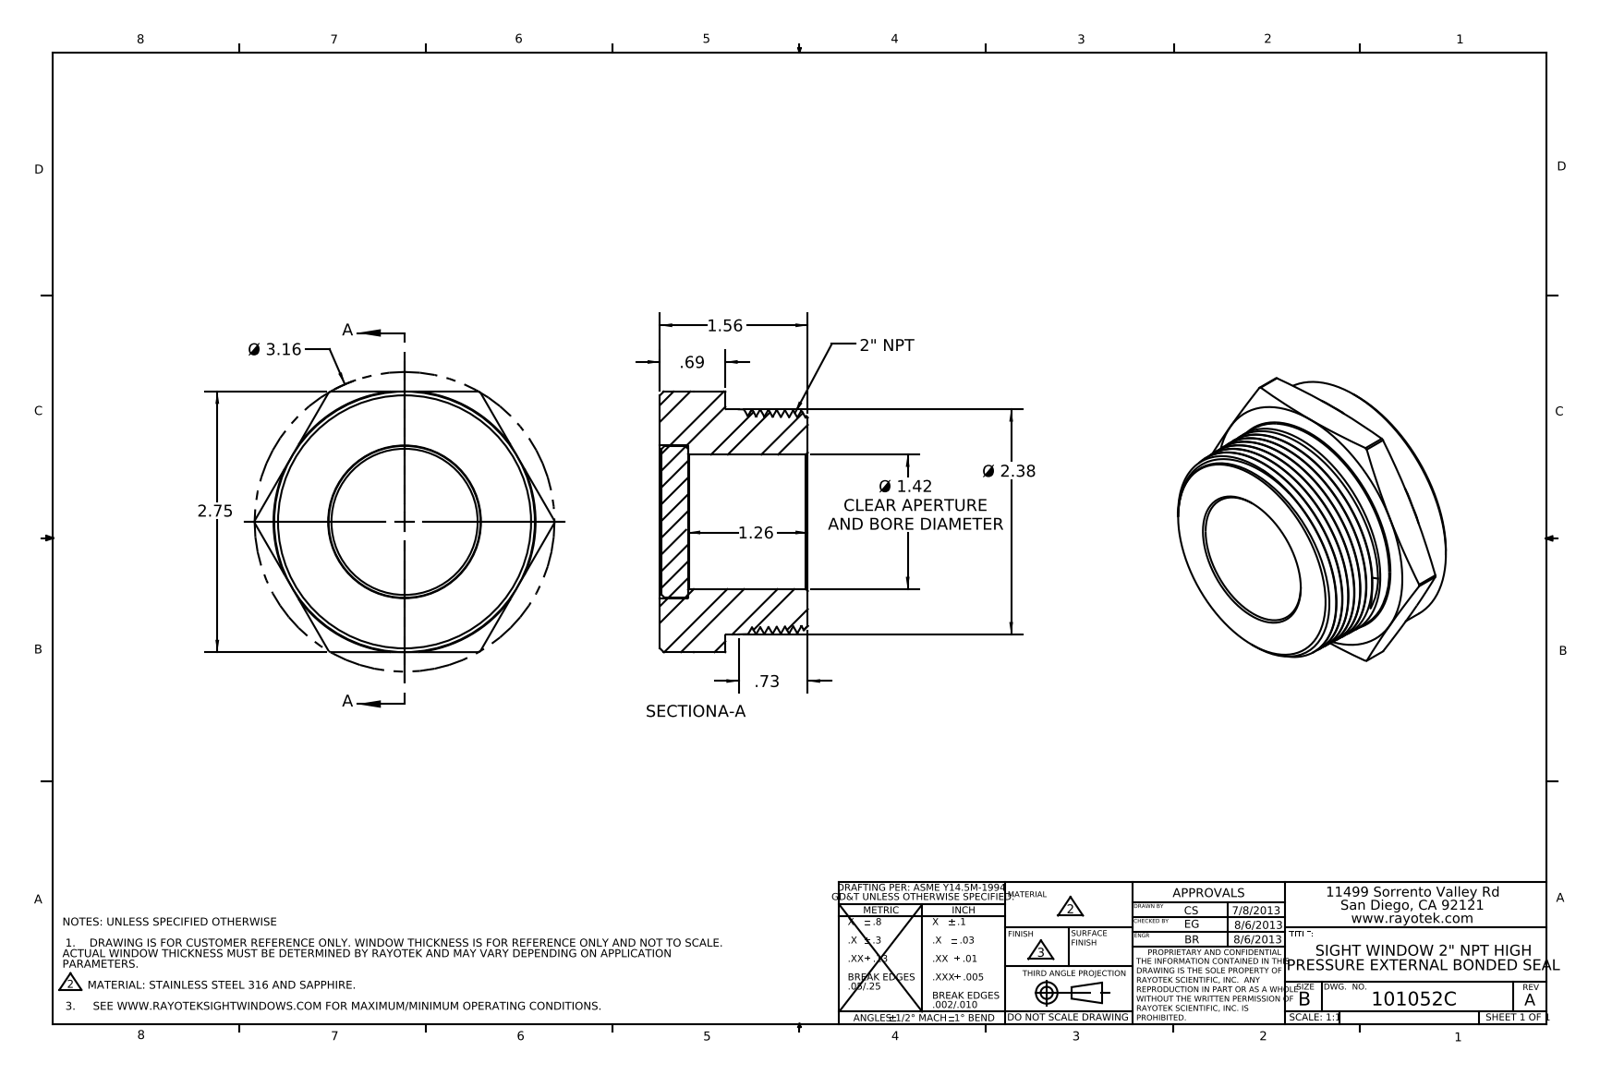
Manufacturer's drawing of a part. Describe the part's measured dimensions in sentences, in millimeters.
The part is named "101052; 402052; 403052". Its 3-D file was written by "SolidWorks 2012 (AUTOMOTIVE_DESIGN)". It is 2 solids with 89 faces: 15 planar, 17 cylindrical and 57 other. Overall it measures 80.3 by 69.9 by 39.6 millimeters. Its volume is 96 000 cubic millimeters and its surface area 24 360 square millimeters. Round holes: 1 of diameter 36.1, 1 of diameter 40.9. Round bosses or shafts: 1 of diameter 69.8, 1 of diameter 60.3, 1 of diameter 40.7. Partial cylindrical surfaces (rounded edges, fillets, slot ends): 1 of radius 40.2. The main face-to-face distances are 7.5, 39.6, 32.1, 0.5, 7, 39.1, 17.5, 17, 10, 22.1.
